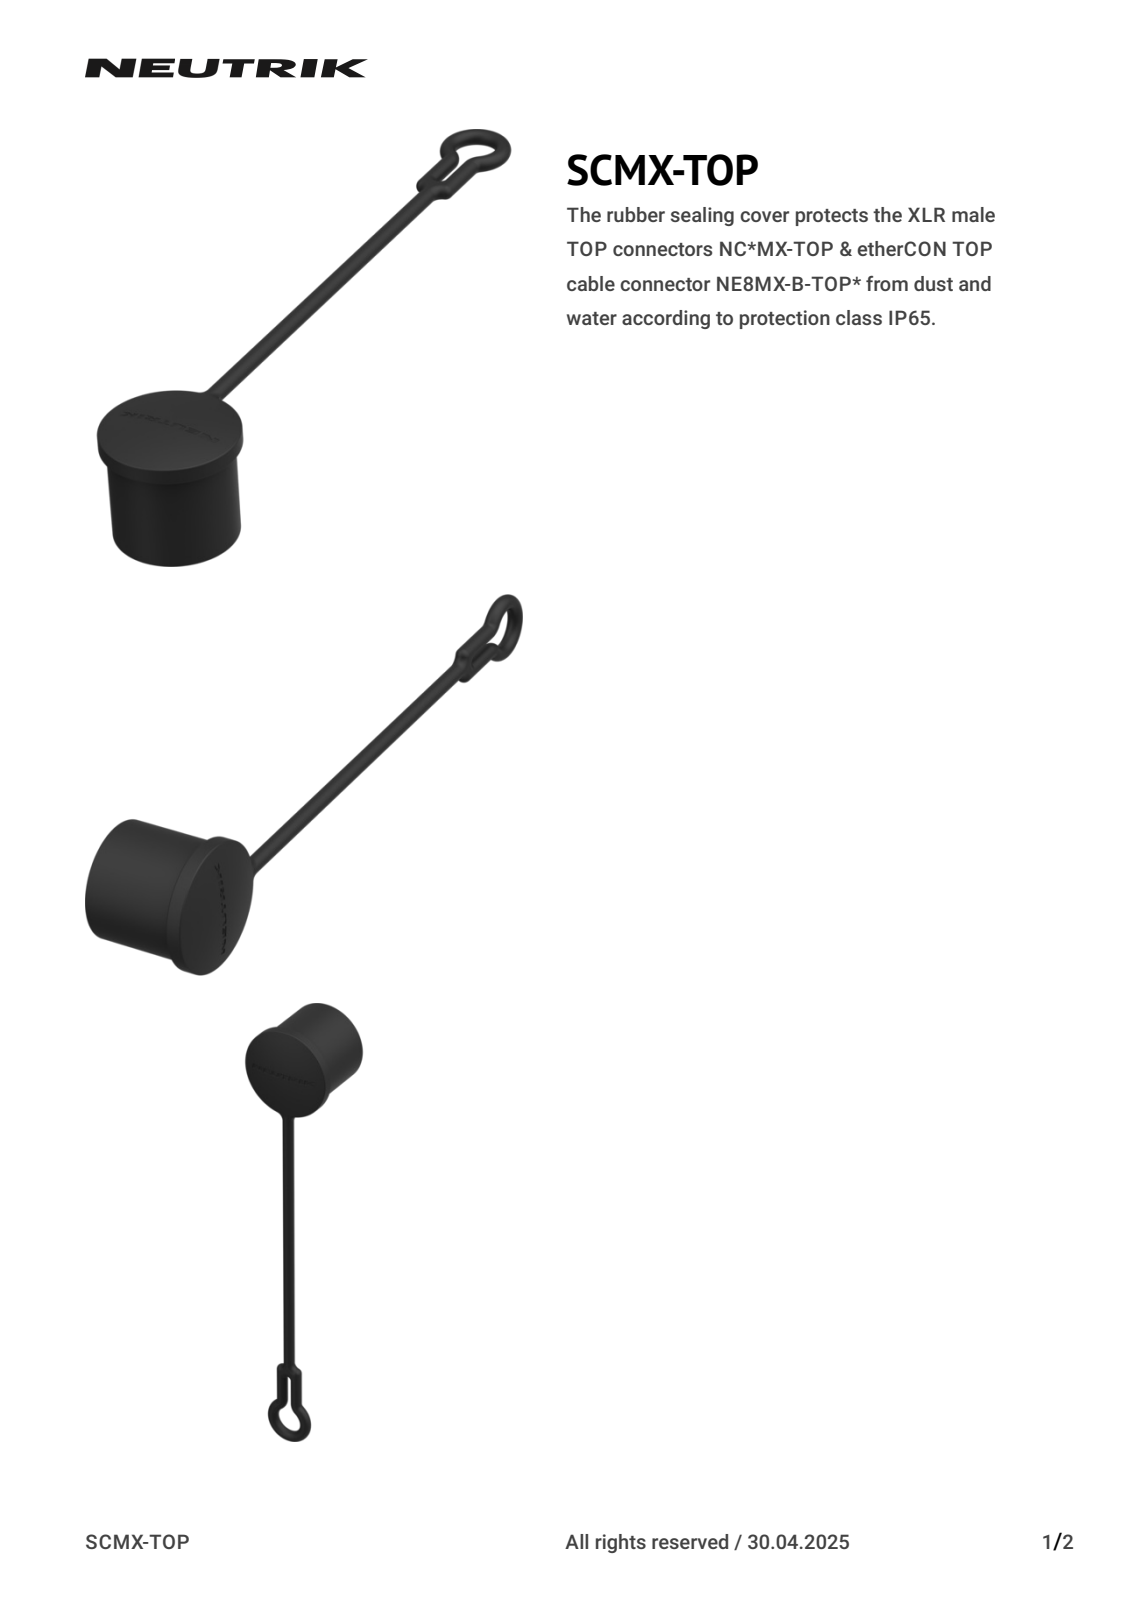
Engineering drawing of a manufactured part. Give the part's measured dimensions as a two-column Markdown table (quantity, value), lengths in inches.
| quantity | value |
| --- | --- |
| part name | SCMX-TOP_07 |
| STEP written by | PRO/ENGINEER BY PARAMETRIC TECHNOLOGY CORPORATION, 2013040 (CONFIG_CONTROL_DESIGN) |
| units | inches |
| bodies | 1 solid, 149 faces (9 planar, 25 cylindrical, 115 other) |
| overall size | 5.089 × 0.984 × 0.886 |
| volume | 0.316 in³ |
| surface area | 8.748 in² |
| round holes (diameter × count) | 0.551 × 1, 0.732 × 1, 0.756 × 1 |
| round bosses / shafts (diameter × count) | 0.118 × 3, 0.984 × 1, 0.882 × 1, 0.63 × 1 |
| main face-to-face distances | 0.709, 0.327, 0.382, 0.118, 0.591, 0.264, 0.445, 0.827 |
